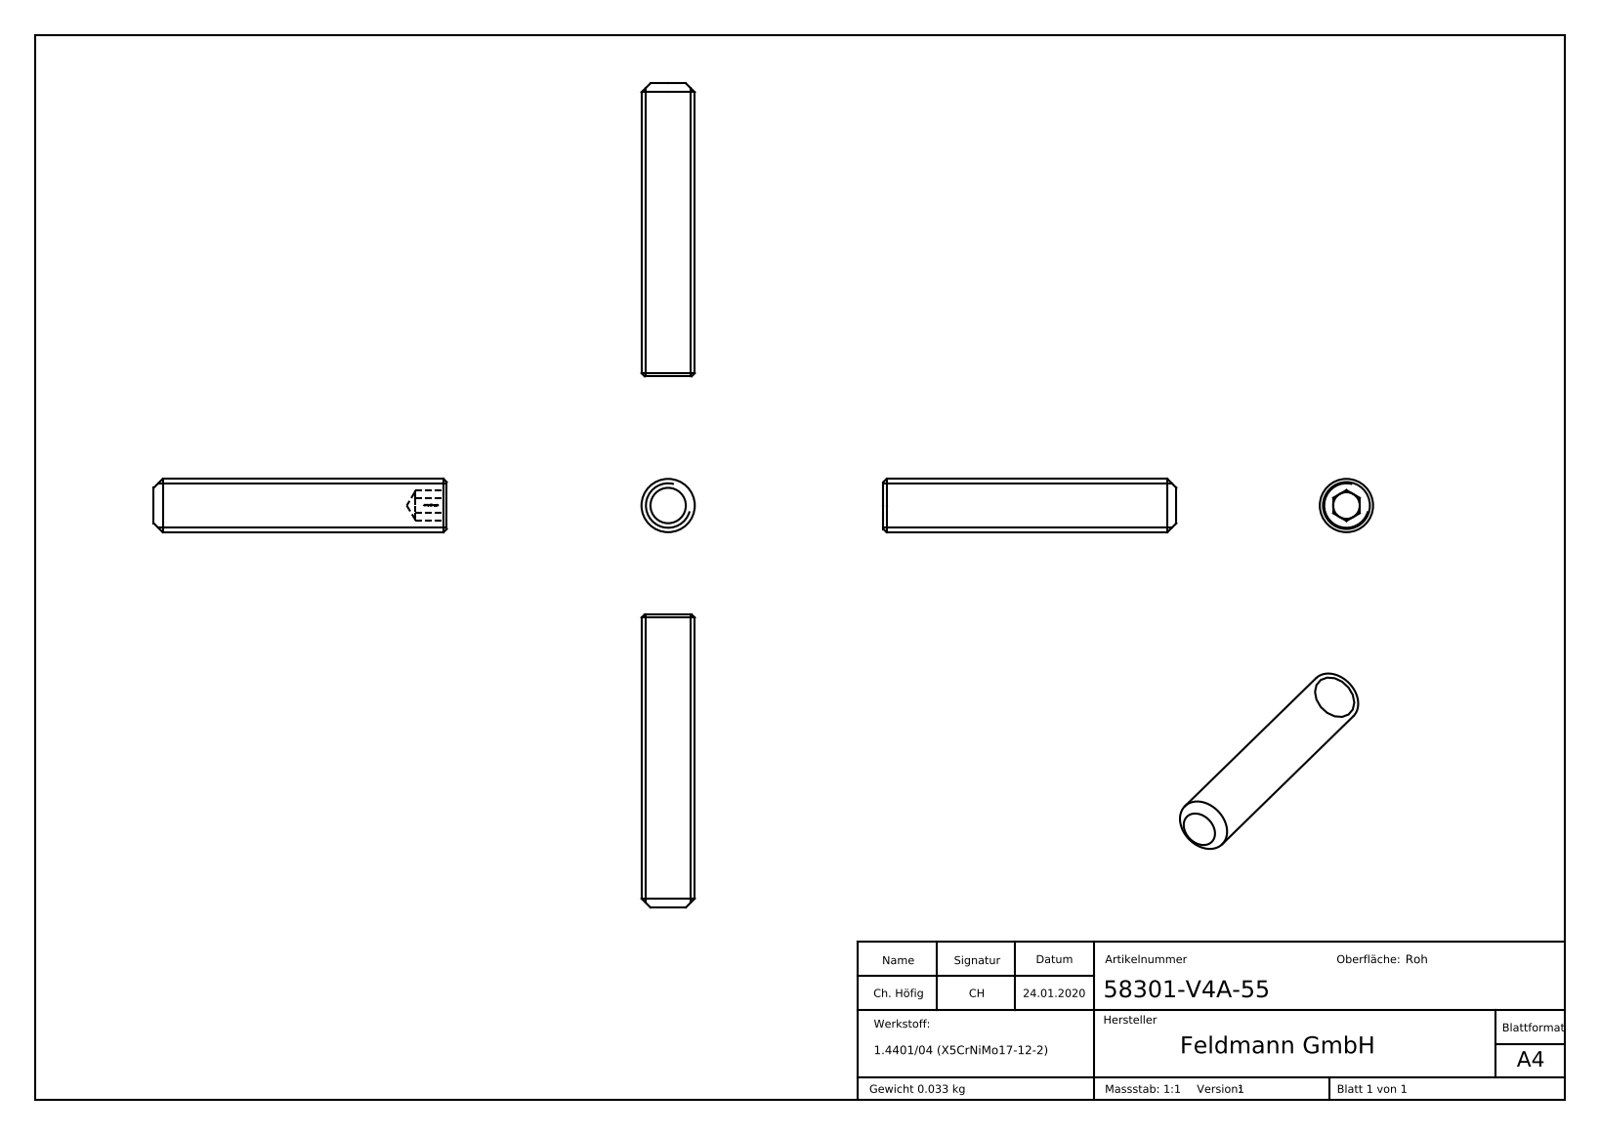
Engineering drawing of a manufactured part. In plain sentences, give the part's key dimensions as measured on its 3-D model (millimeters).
The part is named "58301-V4A-55". Its 3-D file was written by "SolidWorks 2015 (CONFIG_CONTROL_DESIGN)". It is 1 solid with 296 faces: 164 planar, 1 cylindrical and 131 other. Overall it measures 110 by 10 by 10 millimeters. Its volume is 4 135 cubic millimeters and its surface area 1 948 square millimeters. Round bosses or shafts: 1 of diameter 10. The main face-to-face distances are 5, 55, 49, 6, 5.1, 0.4, 0.54, 1.35, 1.78, 0.48.
